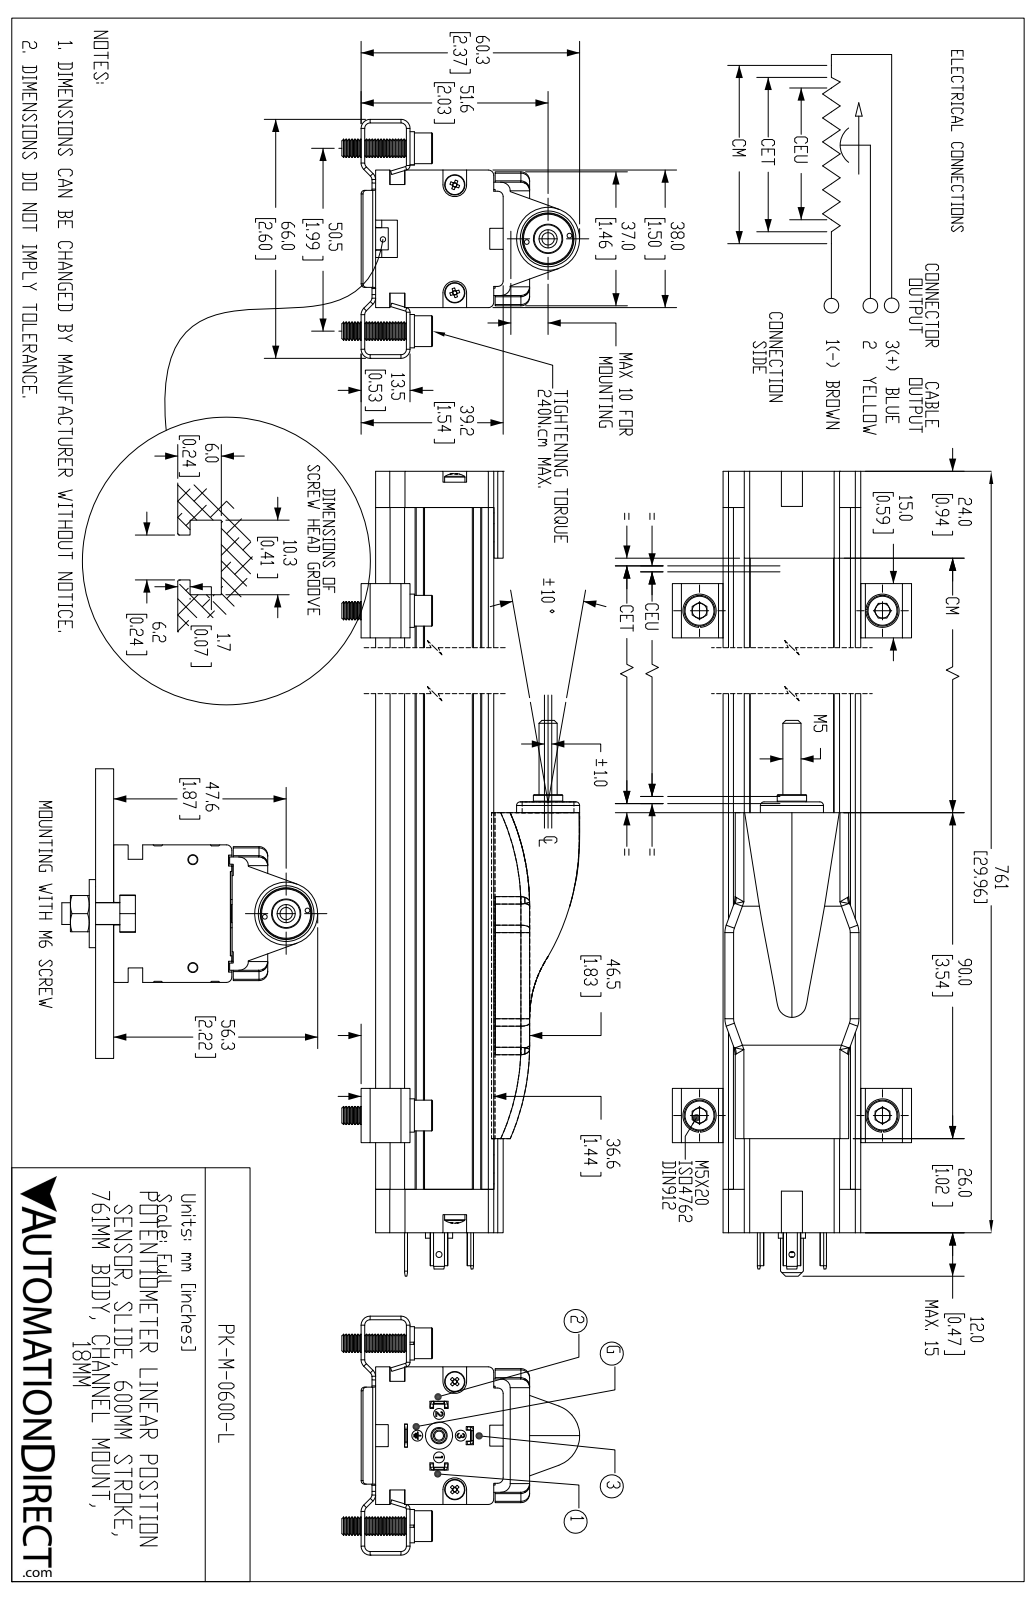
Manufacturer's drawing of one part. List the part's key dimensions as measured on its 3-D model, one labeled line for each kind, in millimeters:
Part name (STEP PRODUCT): PK-M-0600-L
STEP written by: SolidWorks 2019 (AUTOMOTIVE_DESIGN)
Units: millimetres
Bodies: 27 solids, 1761 faces (785 planar, 384 cylindrical, 592 other)
Overall size (bounding box): 773 × 66 × 65.6
Volume: 899 200 mm³ · Surface area: 218 700 mm²
Round holes (diameter × count): ⌀3 ×5, ⌀5.1 ×4, ⌀1.3 ×2, ⌀1.5 ×2, ⌀1.7 ×2, ⌀2.6 ×2, ⌀2.7 ×2, ⌀3.3 ×2, ⌀5.3 ×2, ⌀1.6 ×1, ⌀2.5 ×1, ⌀4 ×1
Round bosses / shafts (diameter × count): ⌀5 ×7, ⌀9.2 ×4, ⌀8.5 ×4, ⌀5.6 ×2, ⌀3 ×2, ⌀2.5 ×2, ⌀17.4 ×1, ⌀14 ×1
Partial cylindrical surfaces — rounded edges, fillets, slot ends (radius × count): R1 ×28, R1.5 ×12, R2.5 ×8, R2.6 ×8, R6 ×8, R0.8 ×6, R2.4 ×6, R0.6 ×4
Main face-to-face distances: 32.2, 4, 32.3, 38, 2, 26.3, 0.5, 8, 6, 0.4
Hole centre spacings: 6, 8.5, 5.9, 9.9, 12, 12.3, 13.7, 15
